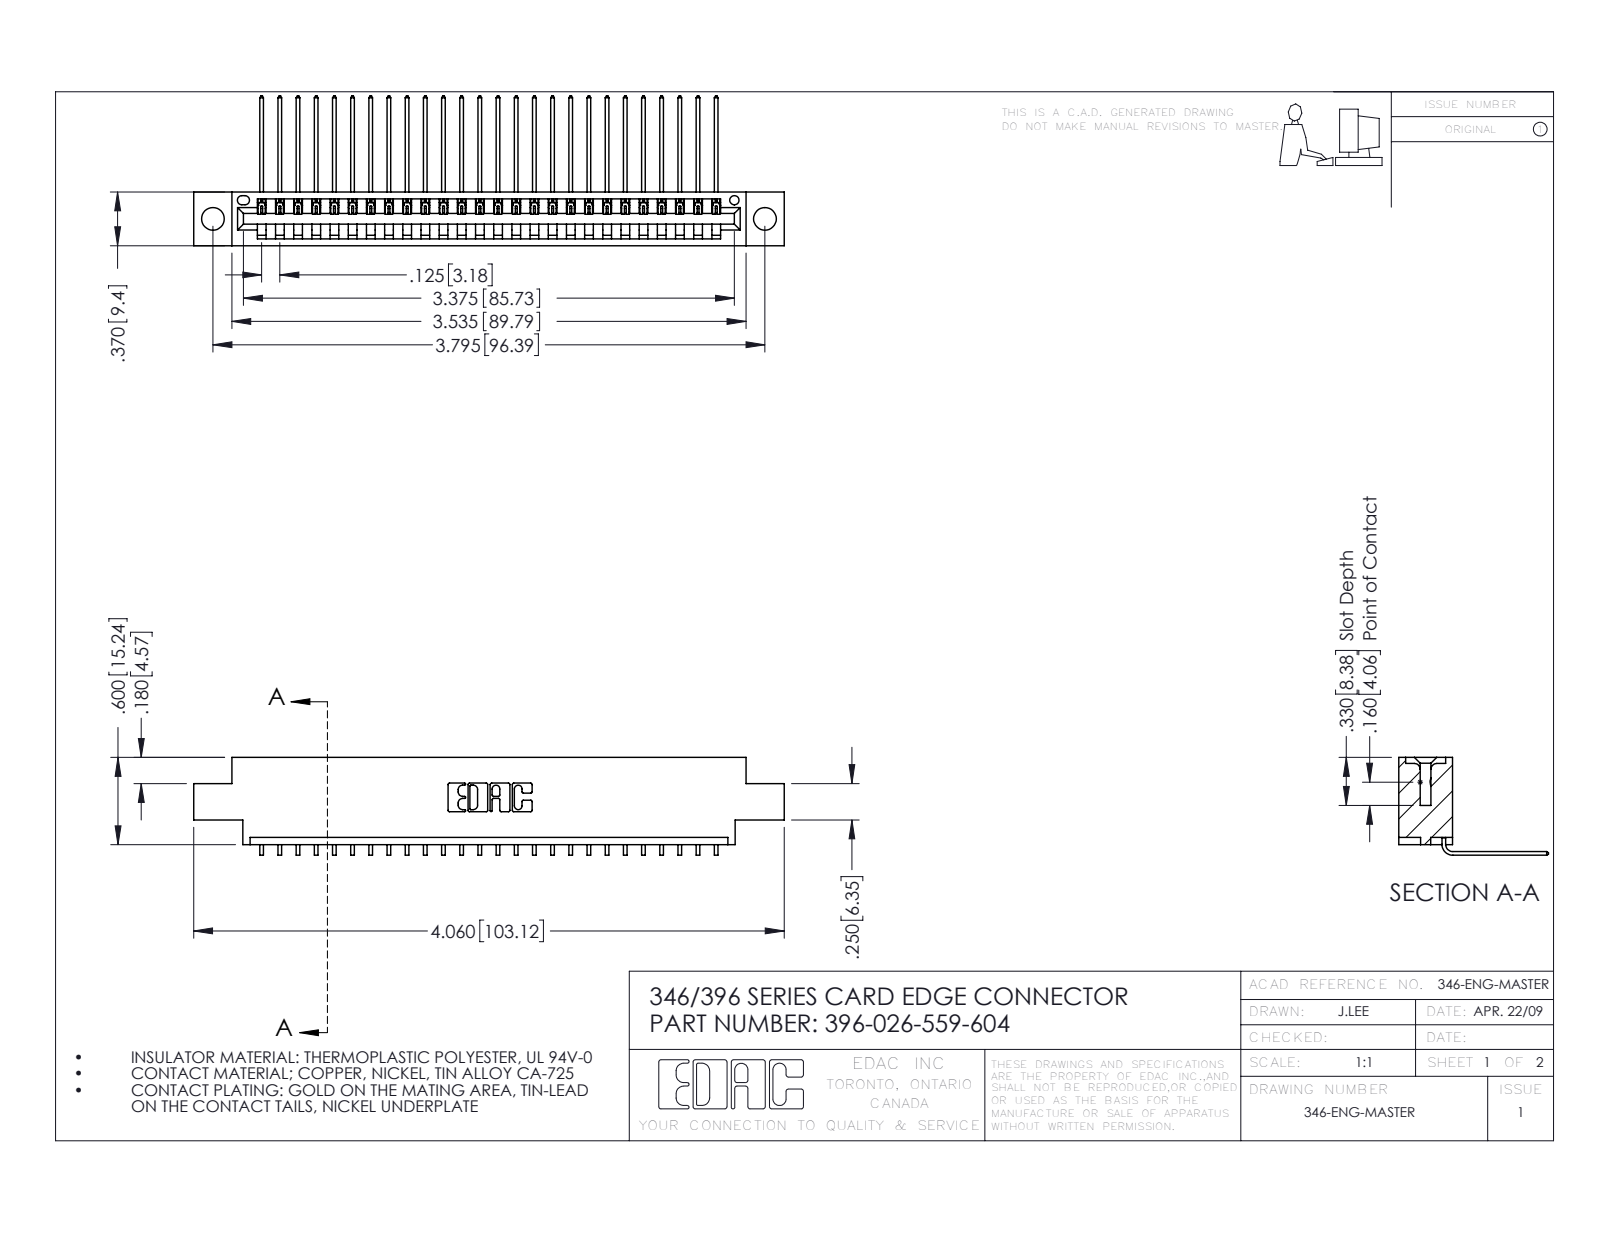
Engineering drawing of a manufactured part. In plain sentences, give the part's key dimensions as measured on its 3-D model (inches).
The part is named "396-026-559-604; 345-292-001_558 559 Tail - 1; 346 Part_0.170 Offset - 0.156 Dia-TH". Its 3-D file was written by "SolidWorks 2016 (CONFIG_CONTROL_DESIGN)". It is 27 solids with 1686 faces: 1172 planar, 514 cylindrical and 0 other. Overall it measures 4.06 by 1.03 by 0.673 inches. Its volume is 0.586 cubic inches and its surface area 19.09 square inches. Round holes: 2 of diameter 0.156, 1 of diameter 0.064. Partial cylindrical surfaces (rounded edges, fillets, slot ends): 52 of radius 0.006, 22 of radius 0.01, 6 of radius 0.007, 6 of radius 0.031, 3 of radius 0.026, 2 of radius 0.031, 2 of radius 0.04, 1 of radius 0.014. The main face-to-face distances are 0.048, 0.322, 0.37, 0.25, 0.025, 0.072, 0.148, 0.222, 0.1, 0.174. The hole center spacings are 0.246, 3.587, 3.795.
